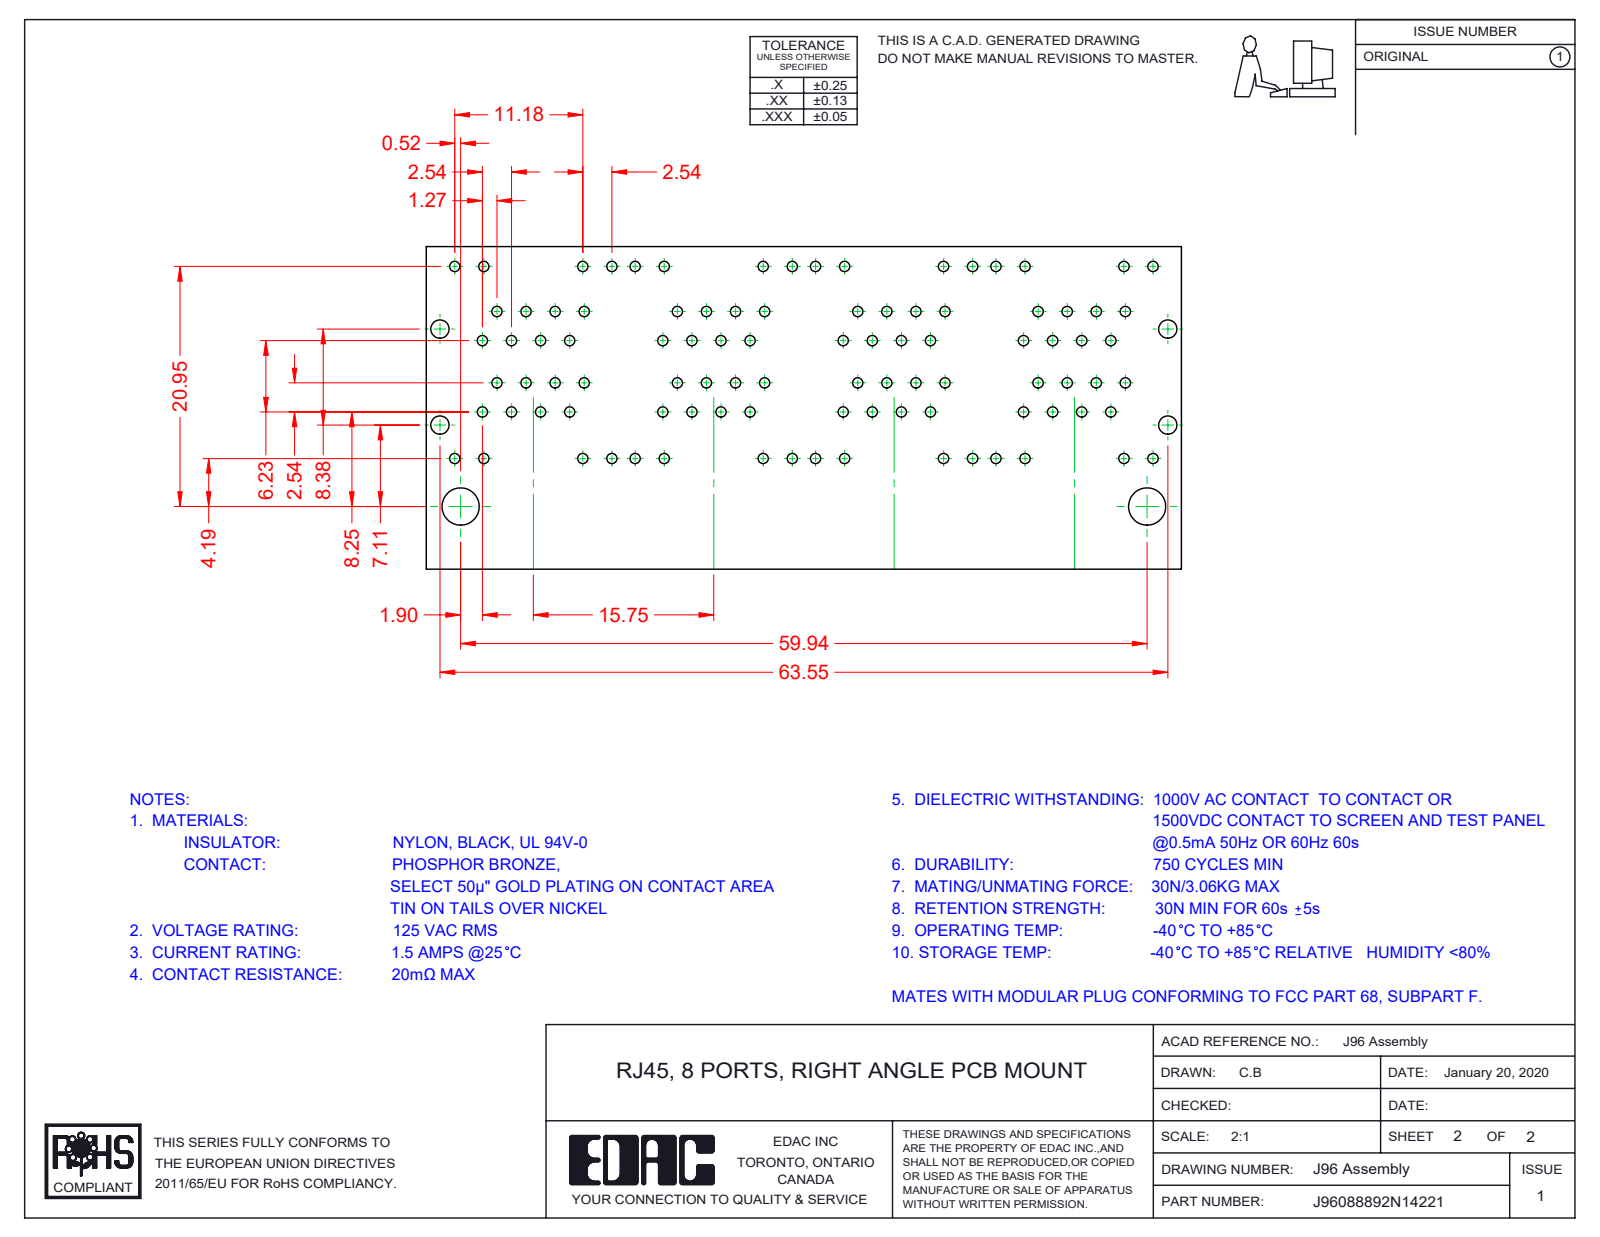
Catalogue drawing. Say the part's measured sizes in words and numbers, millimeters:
The part is named "96 Insulator_8 Ports; 96 LED RH Upper_4-Orange; 96 Contacts Upper; 96 LED LH Upper_1-Yellow (+8 more)". Its 3-D file was written by "SolidWorks 2016 (CONFIG_CONTROL_DESIGN)". It is 96 solids with 7804 faces: 6105 planar, 1388 cylindrical and 311 other. Overall it measures 67.35 by 31.38 by 28.68 millimeters. Its volume is 24 149 cubic millimeters and its surface area 63 596 square millimeters. Round holes: 3 of diameter 1.7. Round bosses or shafts: 3 of diameter 1.68. Partial cylindrical surfaces (rounded edges, fillets, slot ends): 124 of radius 0.25, 73 of radius 0.35, 72 of radius 1, 49 of radius 0.5, 32 of radius 0.91, 27 of radius 0.2, 14 of radius 0.27, 11 of radius 0.7. The main face-to-face distances are 15.75, 0.35, 9.95, 1.17, 1.6, 0.54, 9.98, 10.18, 12.67, 3.37. The hole center spacings are 15.75, 31.5.
